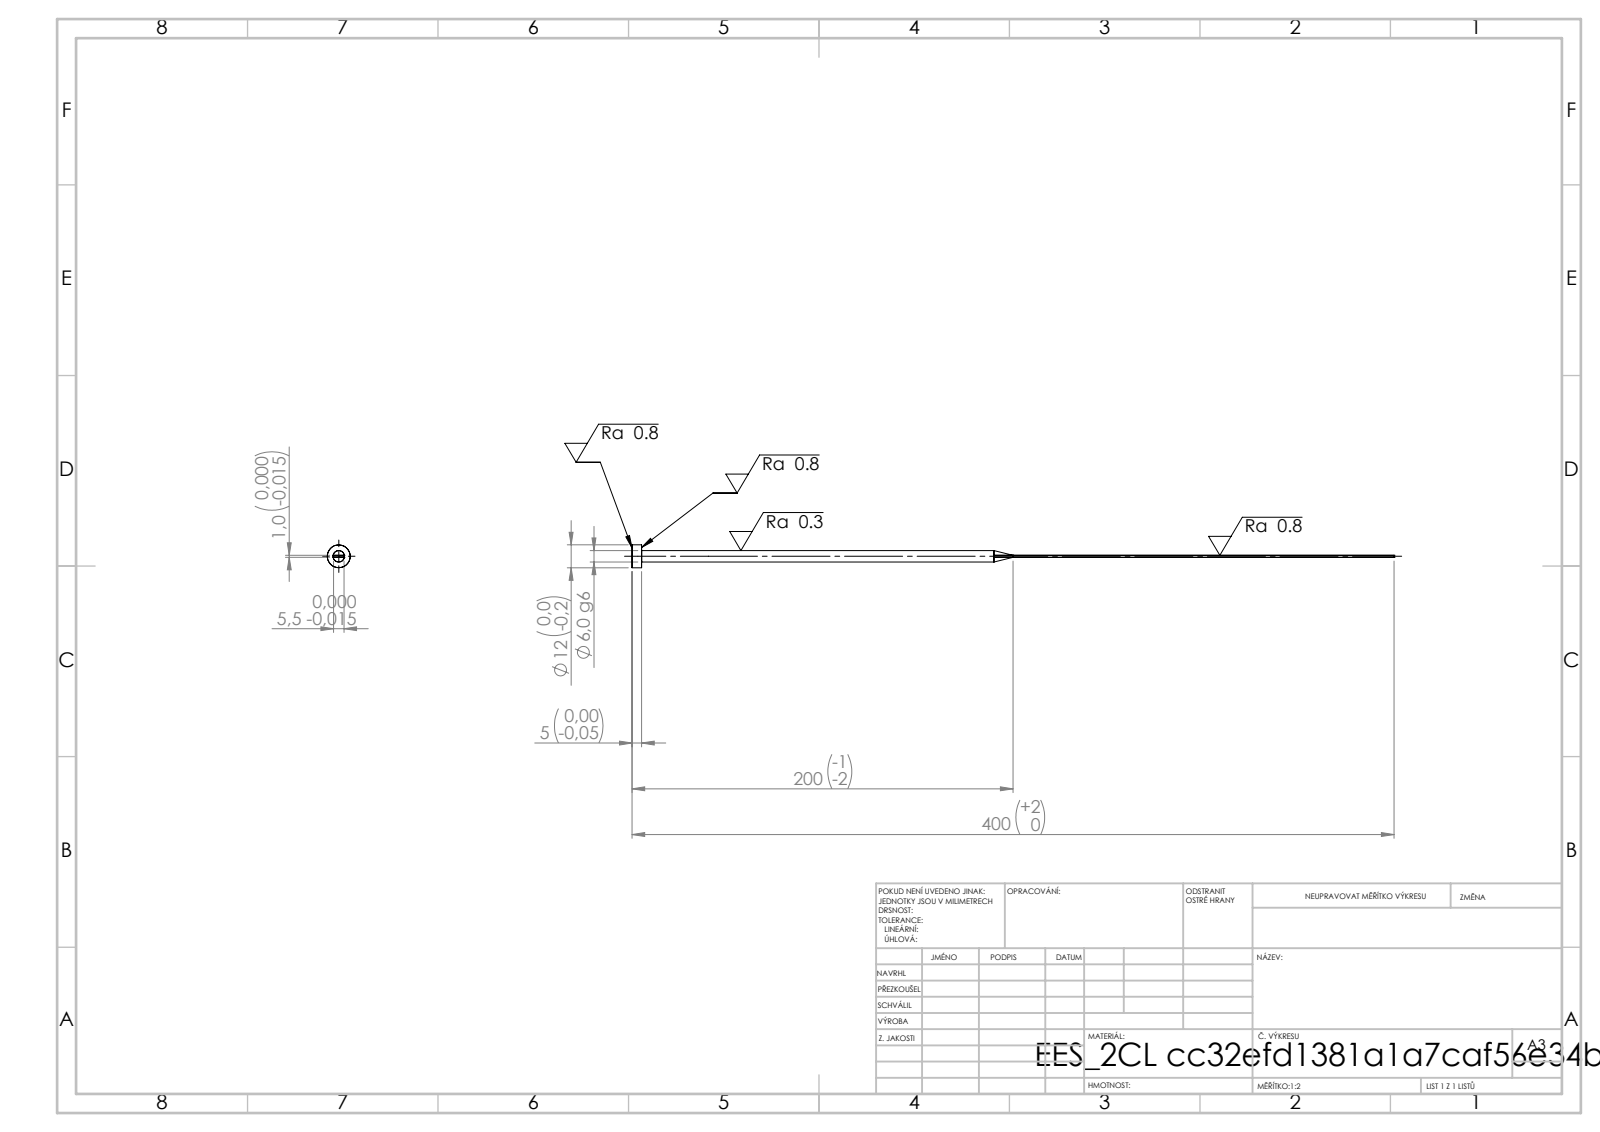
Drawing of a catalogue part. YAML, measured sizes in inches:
step_written_by: "SolidWorks 2019 (CONFIG_CONTROL_DESIGN)"
units: inches
bodies: {solids: 1, faces: 15, planar: 7, cylindrical: 4, other: 4}
overall_size: [15.748, 0.472, 0.472]
volume: 0.431
surface_area: 10.28
round_bosses_or_shafts:
  - {diameter: 0.472, count: 1}
  - {diameter: 0.236, count: 1}
face_to_face_distances: [0.039, 0.217, 0.197, 15.748, 15.551]
